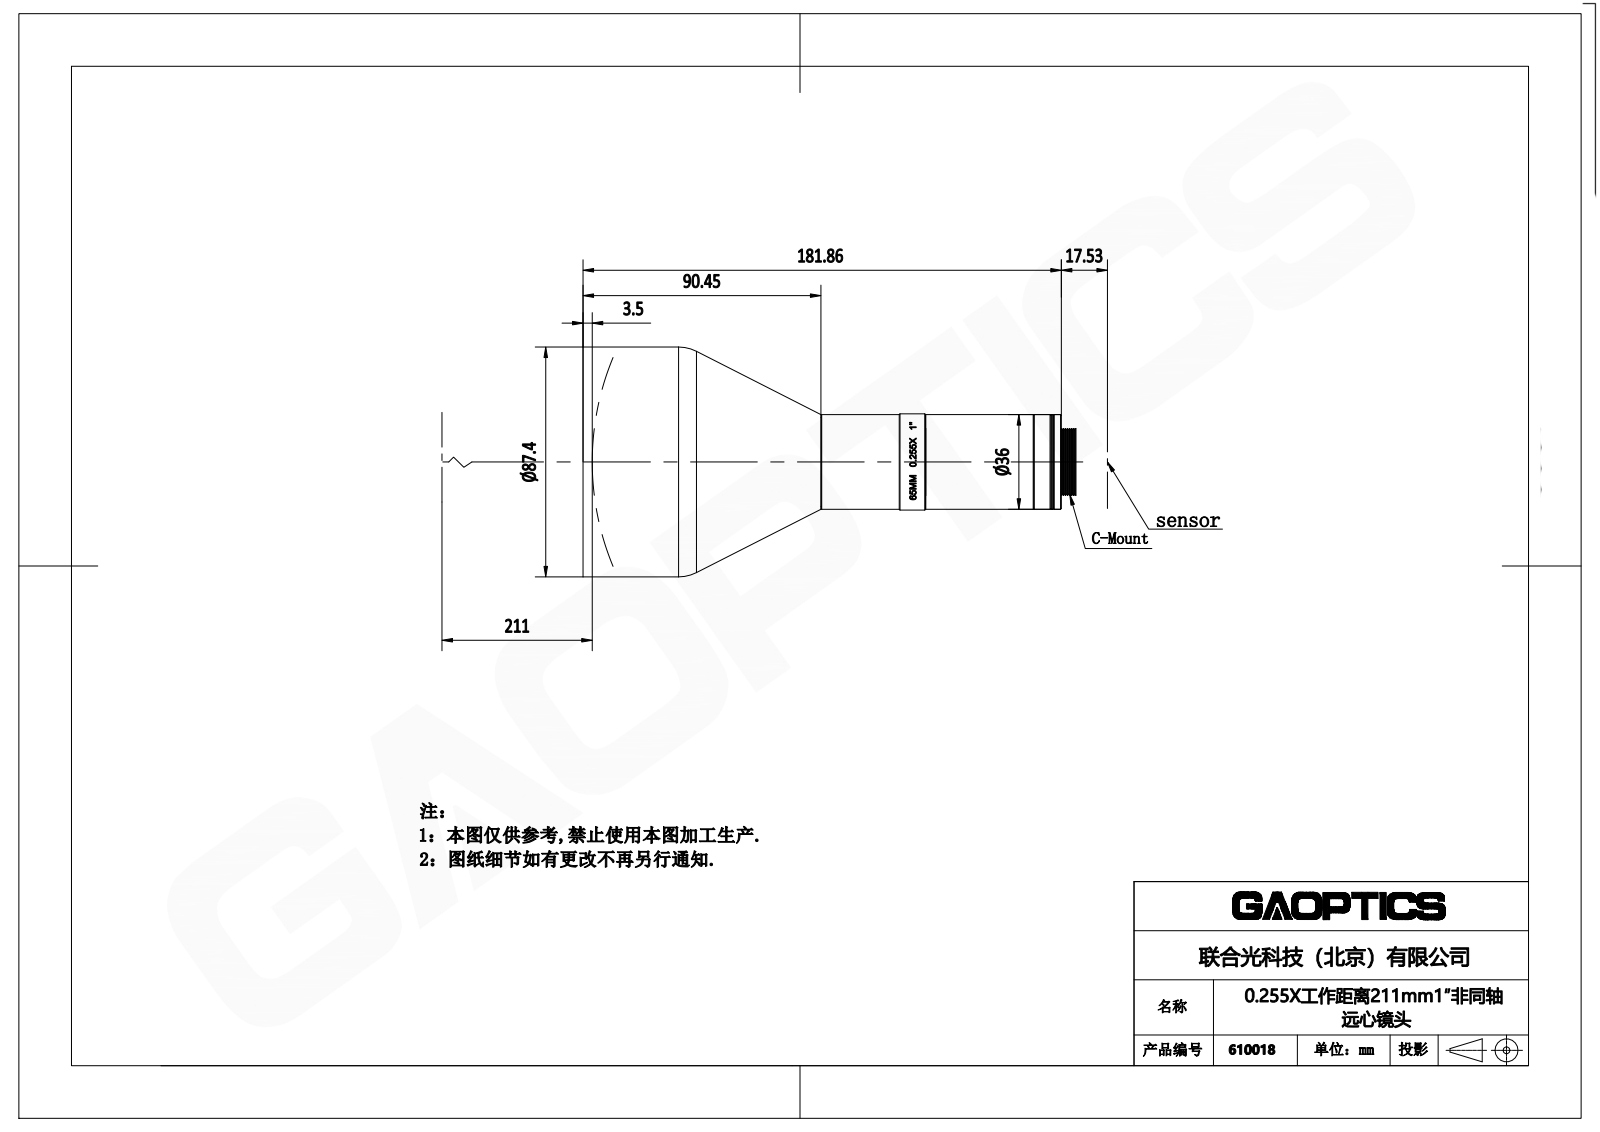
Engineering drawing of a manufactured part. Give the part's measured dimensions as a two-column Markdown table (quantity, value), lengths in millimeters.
| quantity | value |
| --- | --- |
| part name | 610018 |
| STEP written by | SolidWorks 2016 (AUTOMOTIVE_DESIGN) |
| units | millimeters |
| bodies | 0 solids, 73 faces (12 planar, 21 cylindrical, 40 other) |
| overall size | 187.18 × 87.4 × 87.4 |
| round holes (diameter × count) | 21.8 × 1, 76.4 × 1 |
| round bosses / shafts (diameter × count) | 87.4 × 1, 82 × 1, 36 × 1, 35.75 × 1, 35.74 × 1, 31.6 × 1, 25 × 1 |
| partial cylindrical surfaces (radius × count) | 0.5 × 2 |
| main face-to-face distances | 10.5, 4.5, 6, 187.19, 182.69, 176.69, 181.72, 177.22, 171.22, 5.47 |
